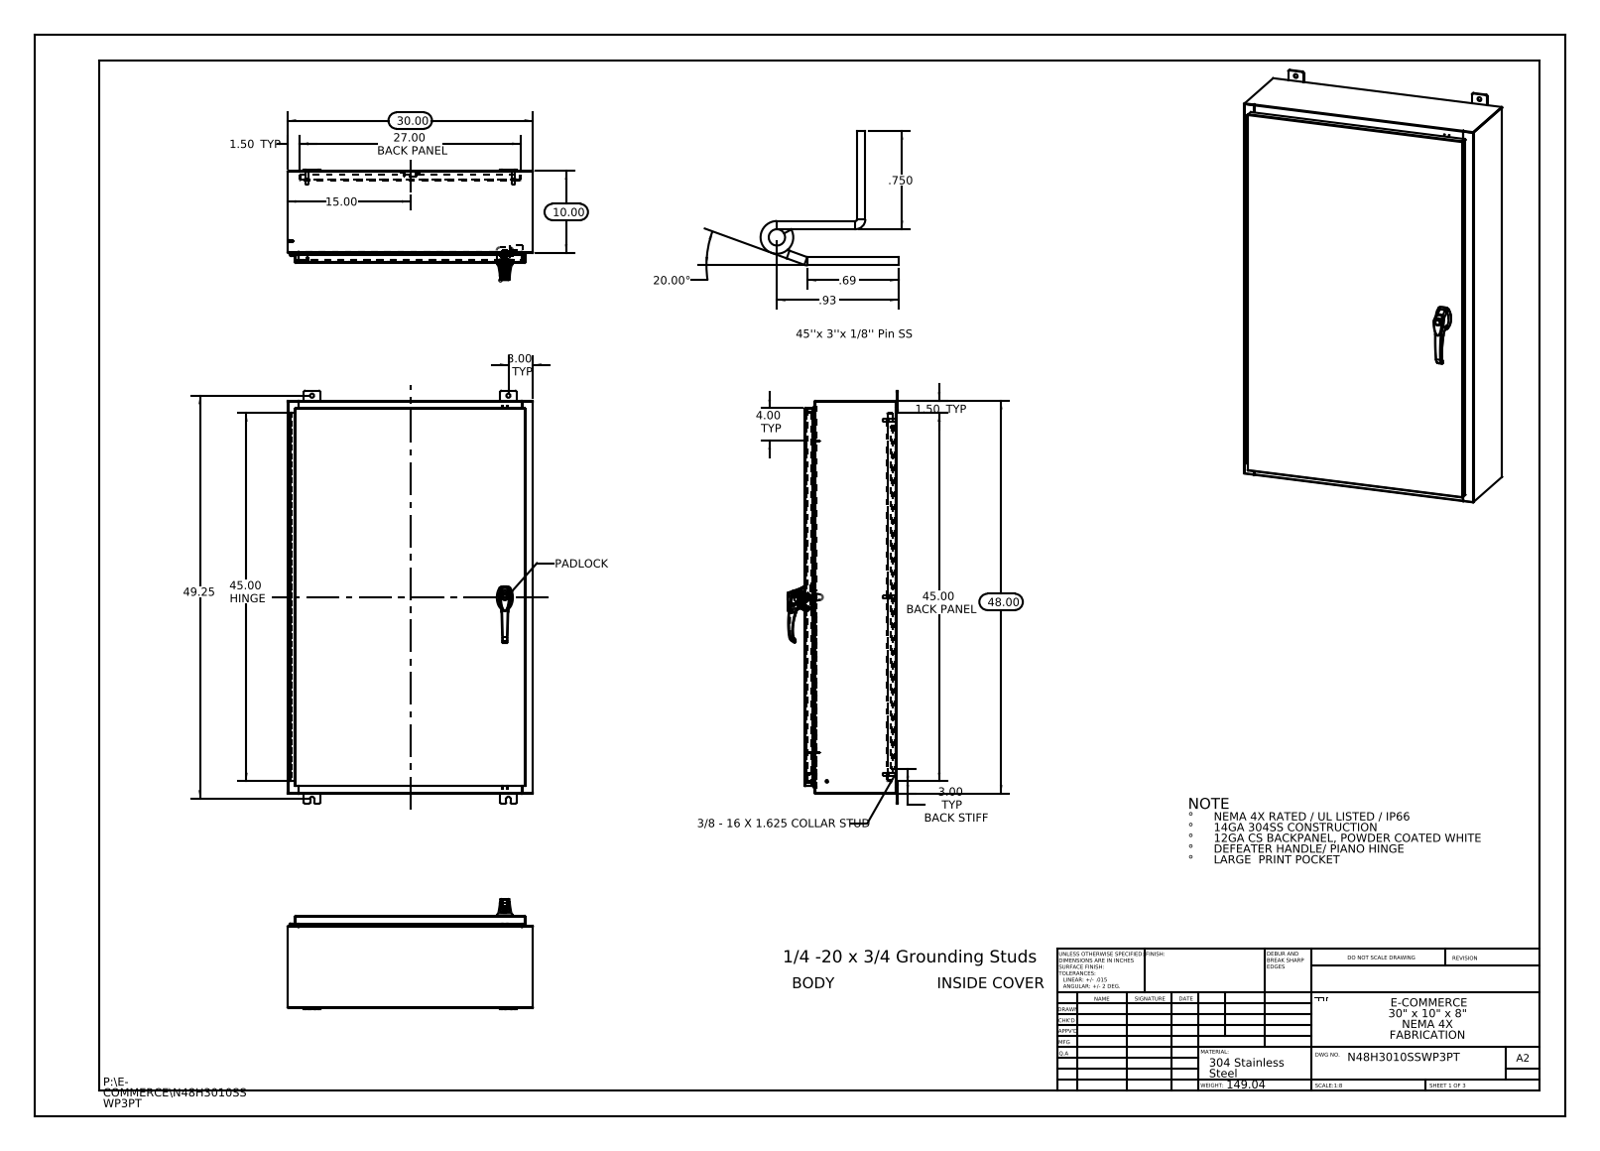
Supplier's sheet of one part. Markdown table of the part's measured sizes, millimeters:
| quantity | value |
| --- | --- |
| part name | 022151; N48H3010SSWP3PT Hinge Cover Side; g26103103_26163303; 00005309_G26103101 (+8 more) |
| STEP written by | SolidWorks 2013 (CONFIG_CONTROL_DESIGN) |
| units | millimeters |
| bodies | 40 solids, 3182 faces (1227 planar, 1237 cylindrical, 718 other) |
| overall size | 1282.7 × 762 × 342.8 |
| volume | 8 623 000 mm³ |
| surface area | 8 406 000 mm² |
| round holes (diameter × count) | 12.7 × 10, 6.4 × 4, 3.5 × 3, 4.1 × 3, 2 × 2, 5.2 × 2, 8 × 2, 11.1 × 2, 3.2 × 1, 3.2 × 1, 5 × 1, 7 × 1 |
| round bosses / shafts (diameter × count) | 15.9 × 6, 9.5 × 6, 8.4 × 6, 4 × 4, 3.6 × 4, 8 × 3, 6 × 3, 30 × 1 |
| partial cylindrical surfaces (radius × count) | 3 × 37, 0.2 × 33, 0.3 × 28, 4.8 × 24, 2.2 × 22, 1 × 15, 0.7 × 12, 0.2 × 6 |
| main face-to-face distances | 1.9, 282.6, 280.7, 2.6, 284.5, 25.4, 257.2, 27.3, 255.3, 29.9 |
| hole center spacings | 440.9, 499.5, 549.3, 844.4, 641.4, 7.5, 15.9, 21.4 |
